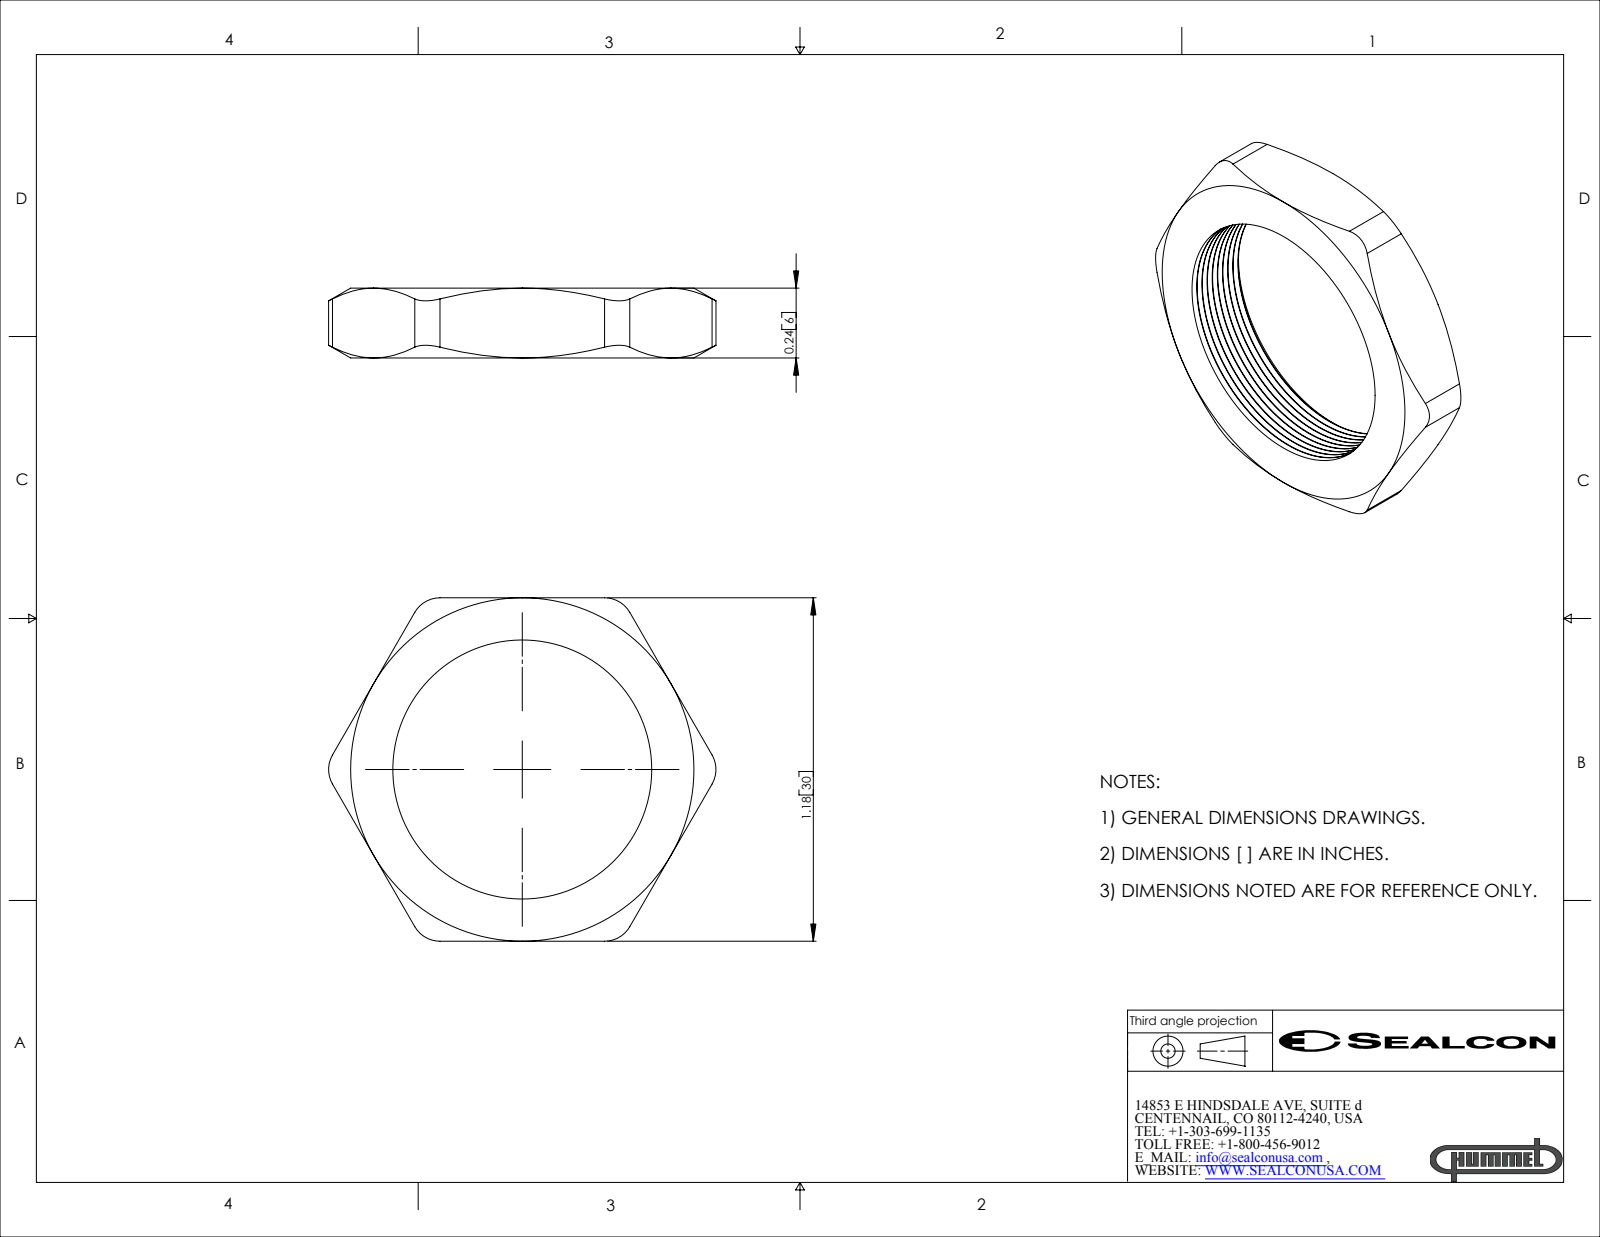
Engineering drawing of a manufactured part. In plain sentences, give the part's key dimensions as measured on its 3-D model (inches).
The part is named "NP-16-GY". Its 3-D file was written by "SolidWorks 2007 (CONFIG_CONTROL_DESIGN)". It is 1 solid with 87 faces: 8 planar, 25 cylindrical and 54 other. Overall it measures 1.332 by 1.18 by 0.24 inches. Its volume is 0.13 cubic inches and its surface area 3.305 square inches. Round holes: 1 of diameter 0.89. Partial cylindrical surfaces (rounded edges, fillets, slot ends): 6 of radius 0.1. The main face-to-face distances are 0.24, 1.18.
